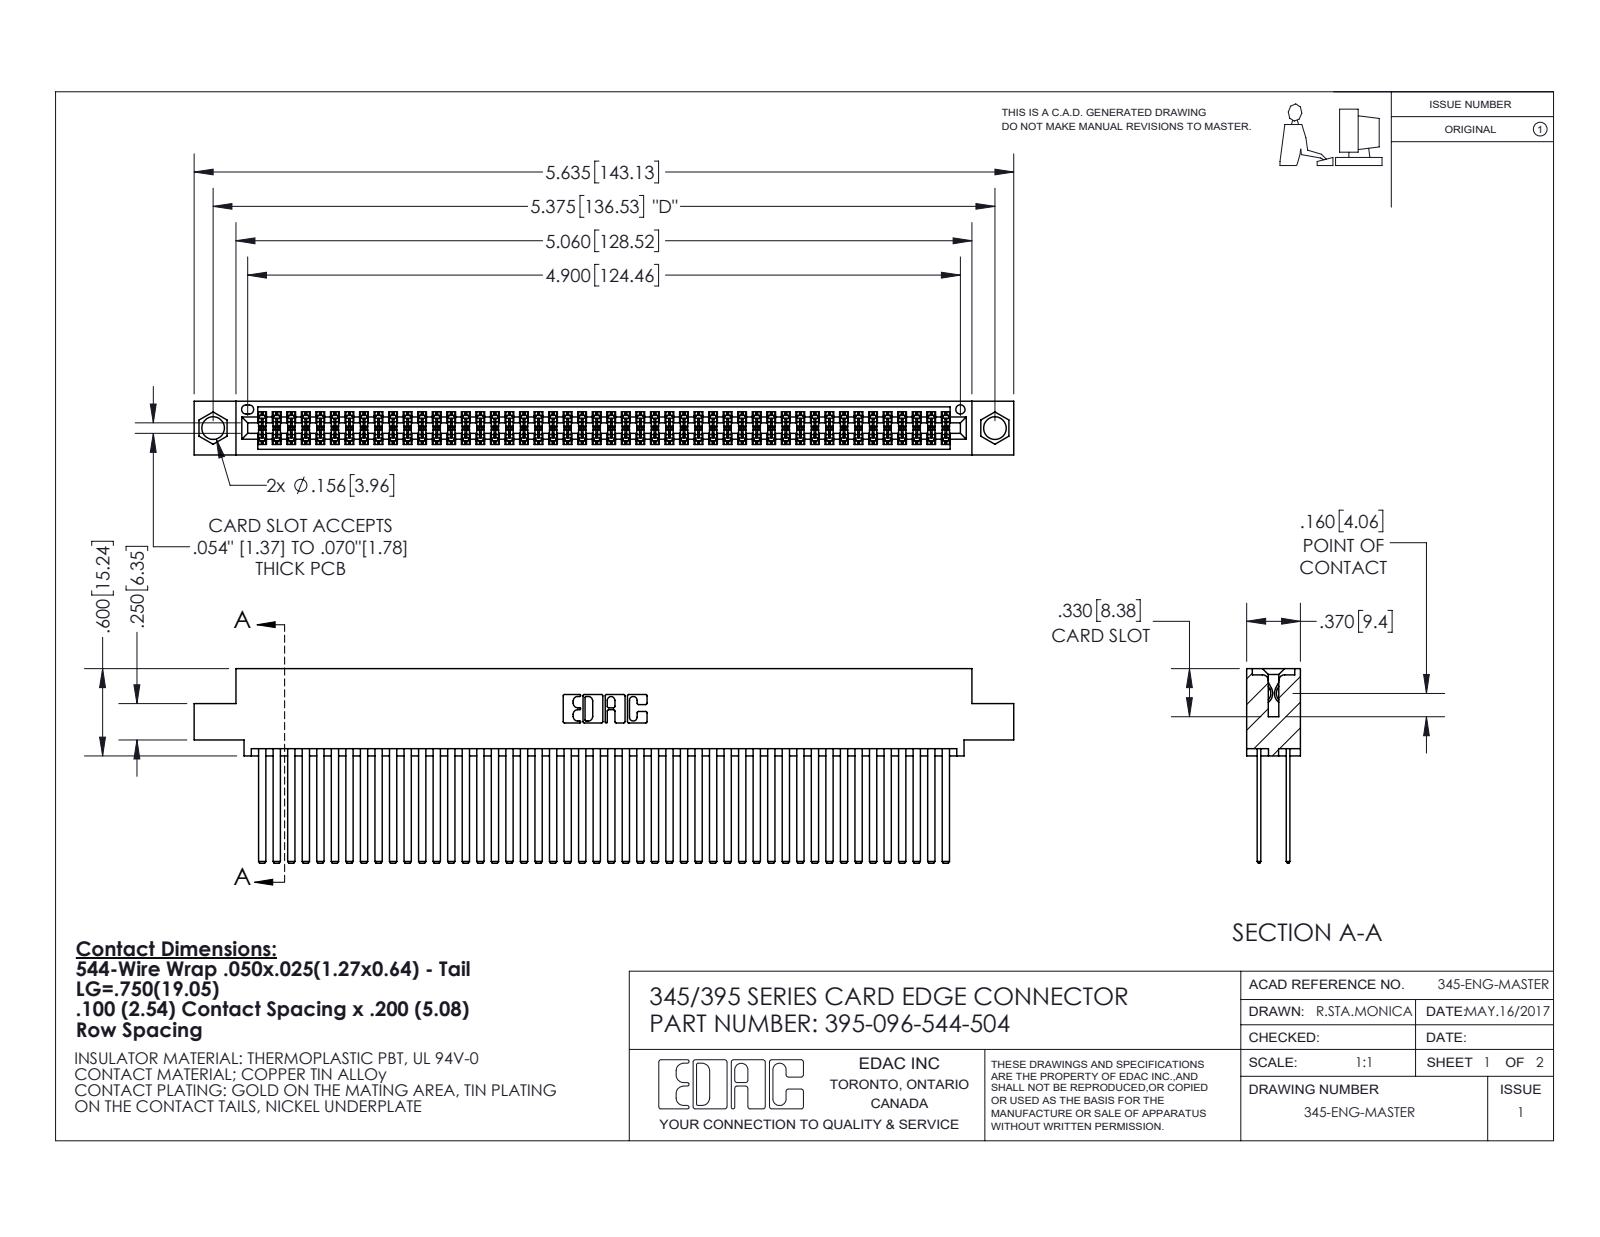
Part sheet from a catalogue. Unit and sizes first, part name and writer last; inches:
Units: inches
Overall size (bounding box): 5.635 × 1.337 × 0.37
Round holes (diameter × count): ⌀0.156 ×2, ⌀0.064 ×1
Partial cylindrical surfaces — rounded edges, fillets, slot ends (radius × count): R0.006 ×144, R0.01 ×22, R0.007 ×6, R0.031 ×6, R0.026 ×3, R0.014 ×2, R0.019 ×2, R0.022 ×2
Main face-to-face distances: 0.2, 0.025, 0.298, 0.072, 0.098, 0.272, 0.225, 0.175, 0.37, 0.05
Hole centre spacings: 0.27, 5.139, 5.375
Volume: 0.923 in³ · Surface area: 40.86 in²
Bodies: 97 solids, 4368 faces (2882 planar, 1486 cylindrical, 0 other)
Part name (STEP PRODUCT): 345 Part_0.110 Offset - 0.156 Dia-TI; 395-096-544-504; 345-292-001_345-293-144
STEP written by: SolidWorks 2020 (CONFIG_CONTROL_DESIGN)
